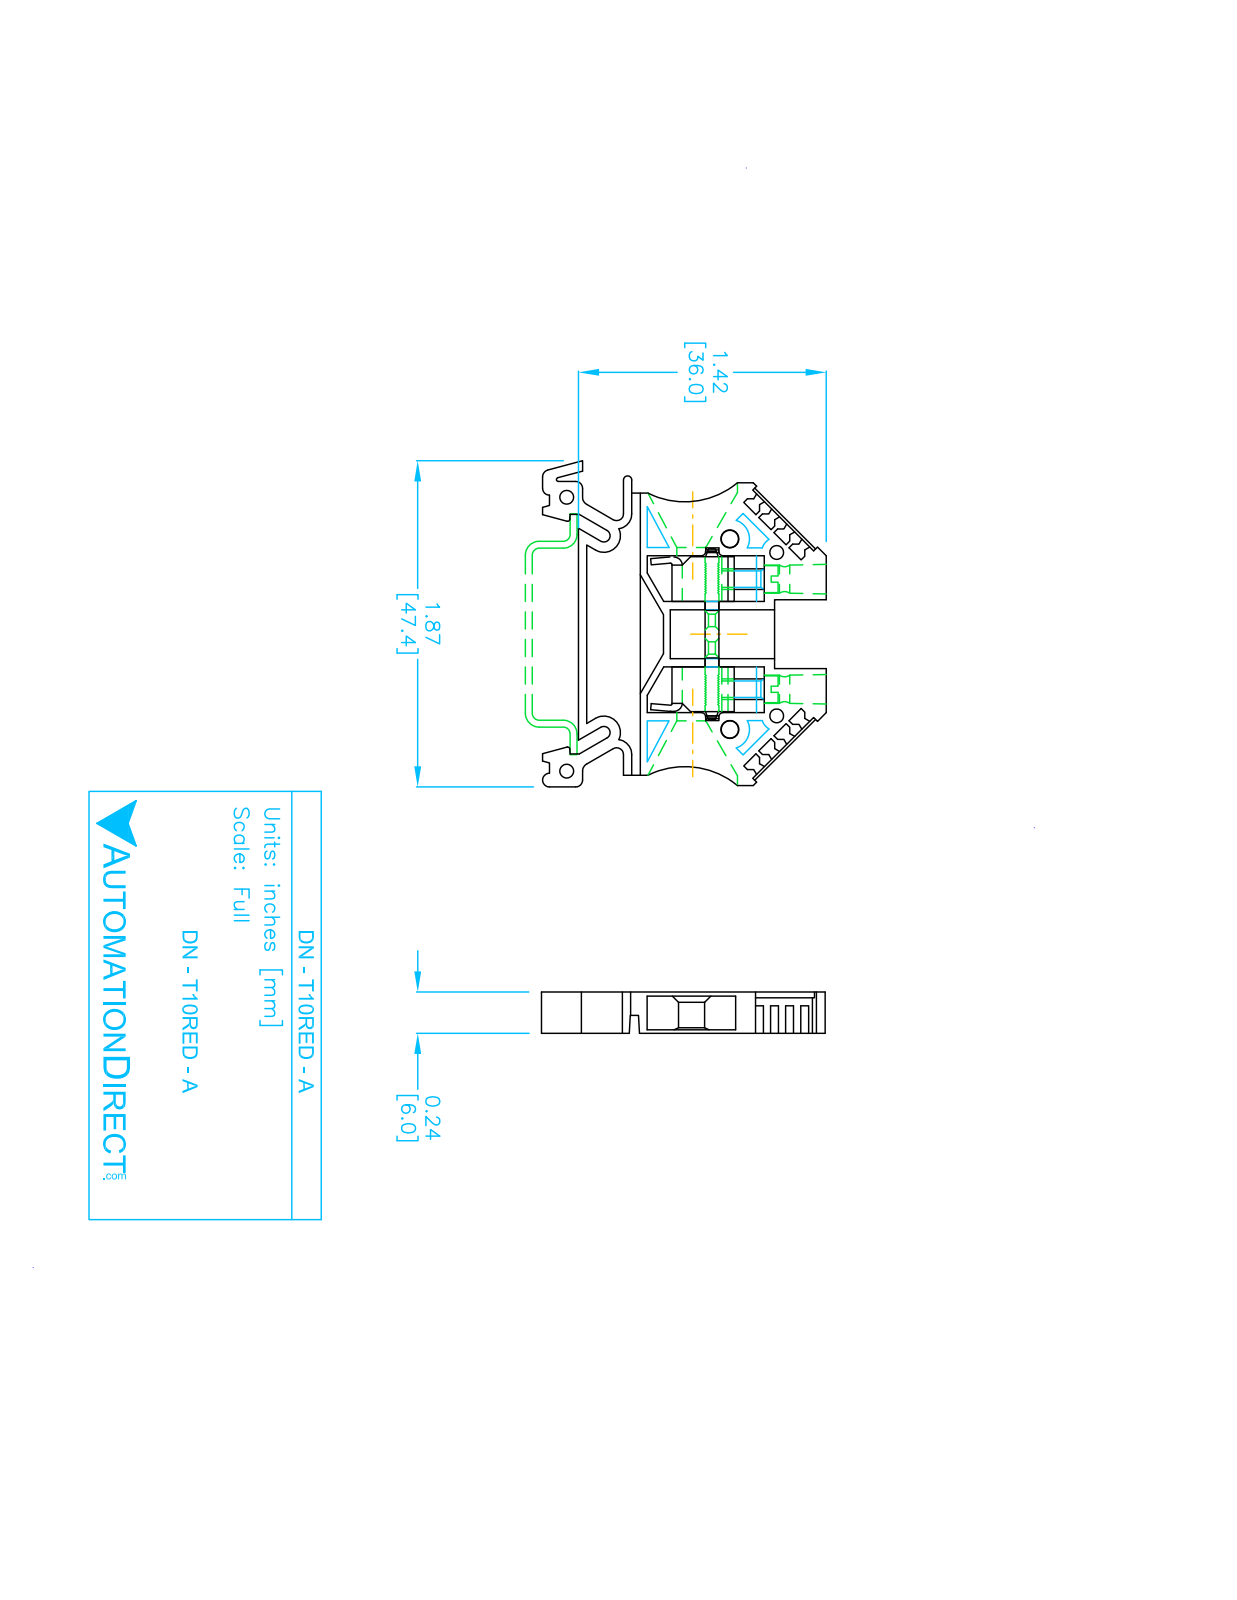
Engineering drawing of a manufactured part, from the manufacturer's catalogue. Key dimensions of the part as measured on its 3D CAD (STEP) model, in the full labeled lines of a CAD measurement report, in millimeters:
Part name (STEP PRODUCT): DN-T10RED-A
STEP written by: SolidWorks 2017 (AUTOMOTIVE_DESIGN)
Units: millimetres
Bodies: 1 solid, 181 faces (141 planar, 40 cylindrical, 0 other)
Overall size (bounding box): 47.4 × 41.2 × 6
Volume: 6 240 mm³ · Surface area: 4 957 mm²
Round holes (diameter × count): ⌀2 ×2, ⌀4.4 ×2
Partial cylindrical surfaces — rounded edges, fillets, slot ends (radius × count): R1 ×7, R0.3 ×2, R0.9 ×2, R1.2 ×2, R2.2 ×2, R2.4 ×2, R12 ×2, R0.3 ×1
Main face-to-face distances: 5.8, 6, 3.6, 2.4, 1.2, 2.2, 3.4, 9, 1.8, 7.8
Hole centre spacings: 16, 39.8
